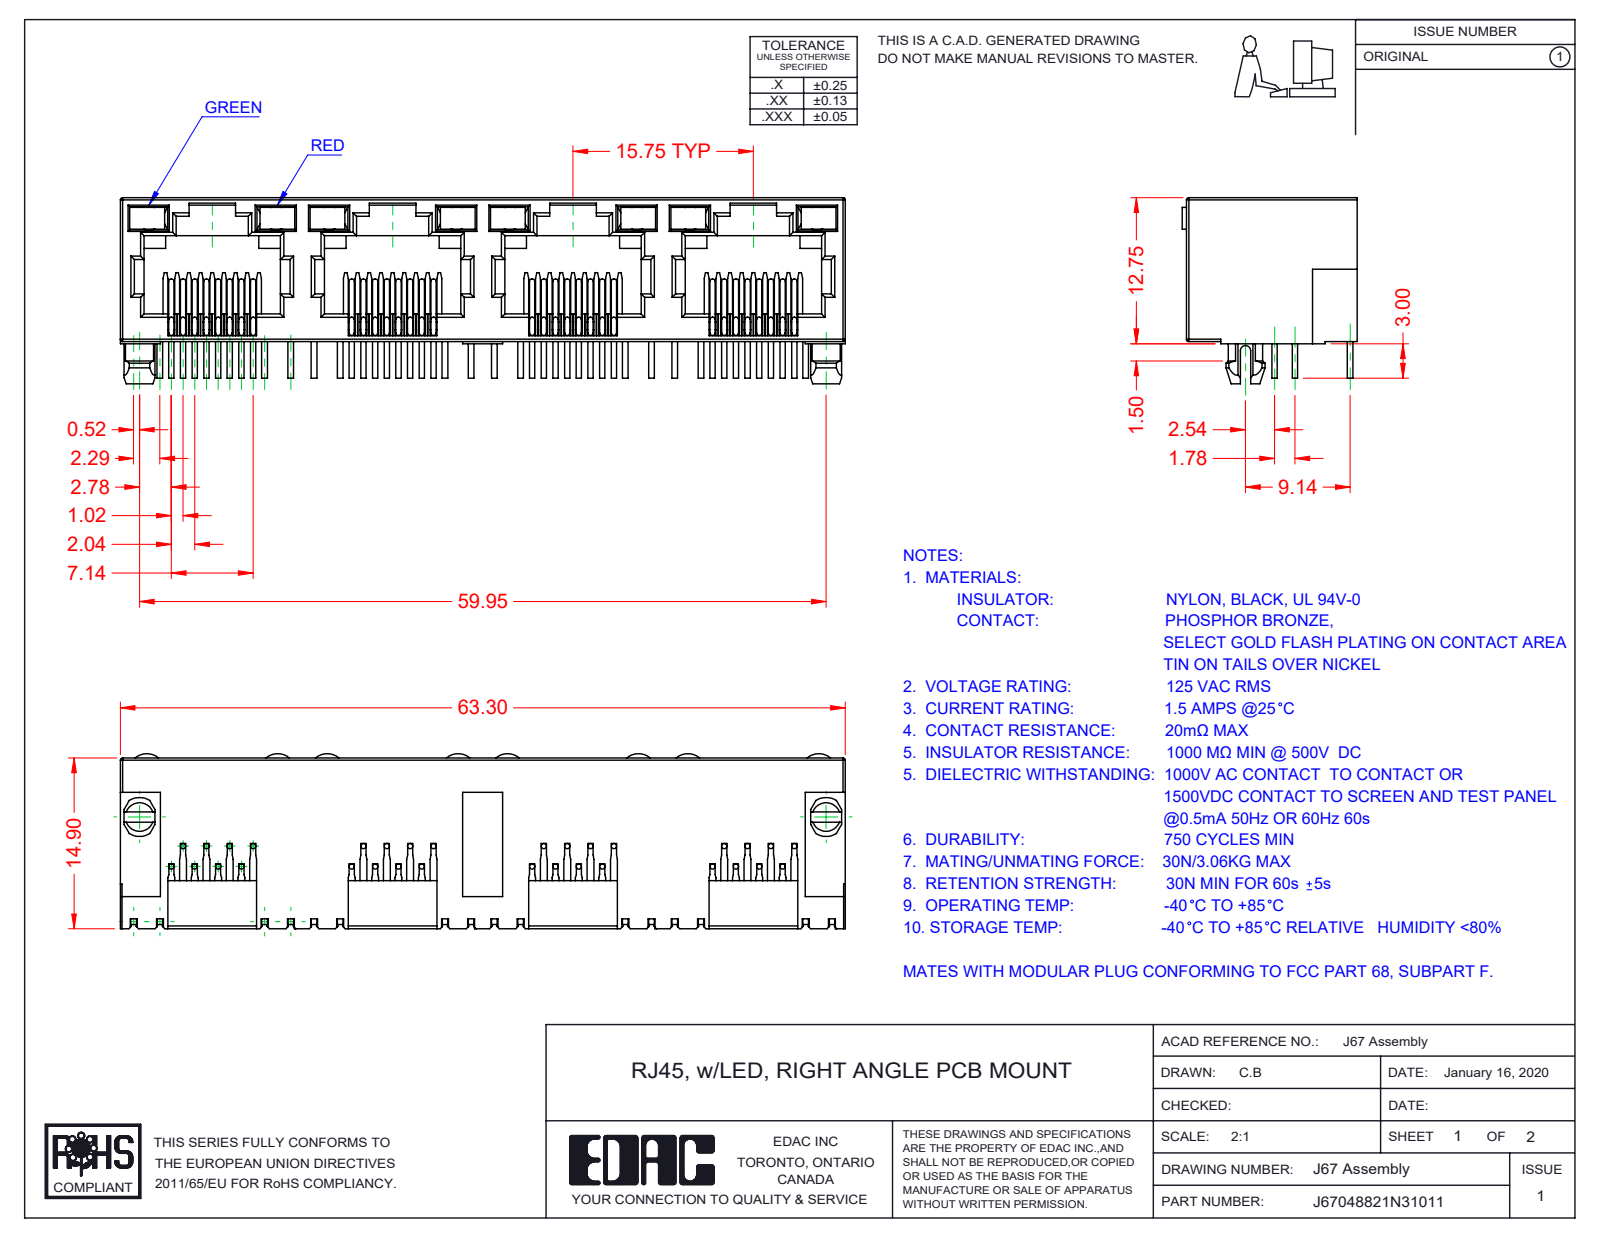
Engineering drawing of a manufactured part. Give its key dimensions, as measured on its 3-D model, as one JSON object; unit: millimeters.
{"part_name": "J67048822N32011; 67 LED LH_3-Green; 67 LED RH_2-Red; 67 Insulator (+1 more)", "step_written_by": "SolidWorks 2016 (CONFIG_CONTROL_DESIGN)", "units": "millimeters", "bodies": {"solids": 41, "faces": 2465, "planar": 1781, "cylindrical": 476, "other": 208}, "overall_size": [63.3, 16.25, 15.28], "volume_mm3": 5159, "surface_area_mm2": 11573, "round_bosses_or_shafts": [[0.46, 96]], "partial_cylinders_radius": [[0.2, 66], [0.3, 29], [0.45, 9], [1.55, 8], [1.5, 2], [1.7, 2], [0.35, 1], [1, 1]], "face_to_face_distances": [0.5, 12.55, 1.89, 0.89, 10, 15.75, 1, 1.39, 11, 11.89]}
